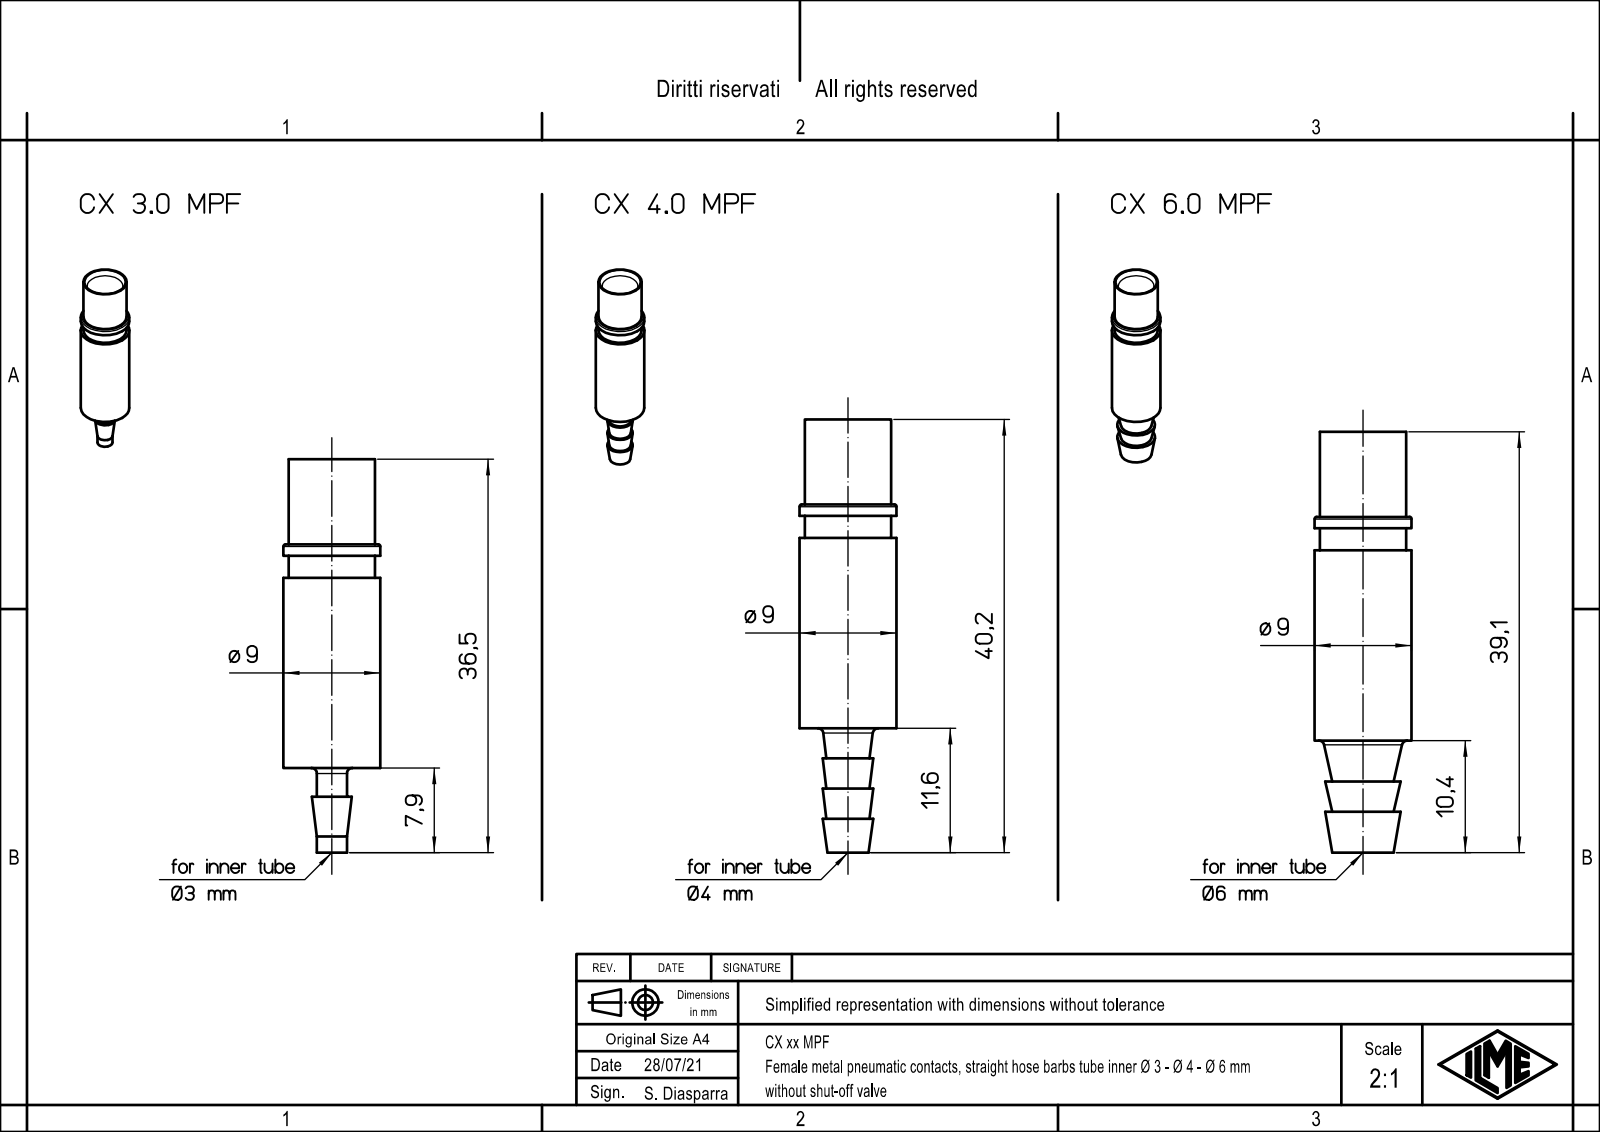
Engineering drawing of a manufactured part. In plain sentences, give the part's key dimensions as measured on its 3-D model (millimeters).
The part is named "CX_3.0_MPF". Its 3-D file was written by "Creo Elements/Direct Modeling 20.1B 02-Apr-2019 (C) Parametric Technology GmbH (AUTOMOTIVE_DESIGN)". It is 1 solid with 41 faces: 7 planar, 18 cylindrical and 16 other. Overall it measures 36.5 by 9 by 9 millimeters. Its volume is 1 179 cubic millimeters and its surface area 1 456 square millimeters. Round holes: 1 of diameter 2, 1 of diameter 4, 1 of diameter 6.6. Round bosses or shafts: 1 of diameter 9, 1 of diameter 8, 1 of diameter 2.8. The main face-to-face distances are 19.7, 17.65, 2.05, 20.75, 3.1, 1.05, 28.65, 11, 8.95, 7.9.
